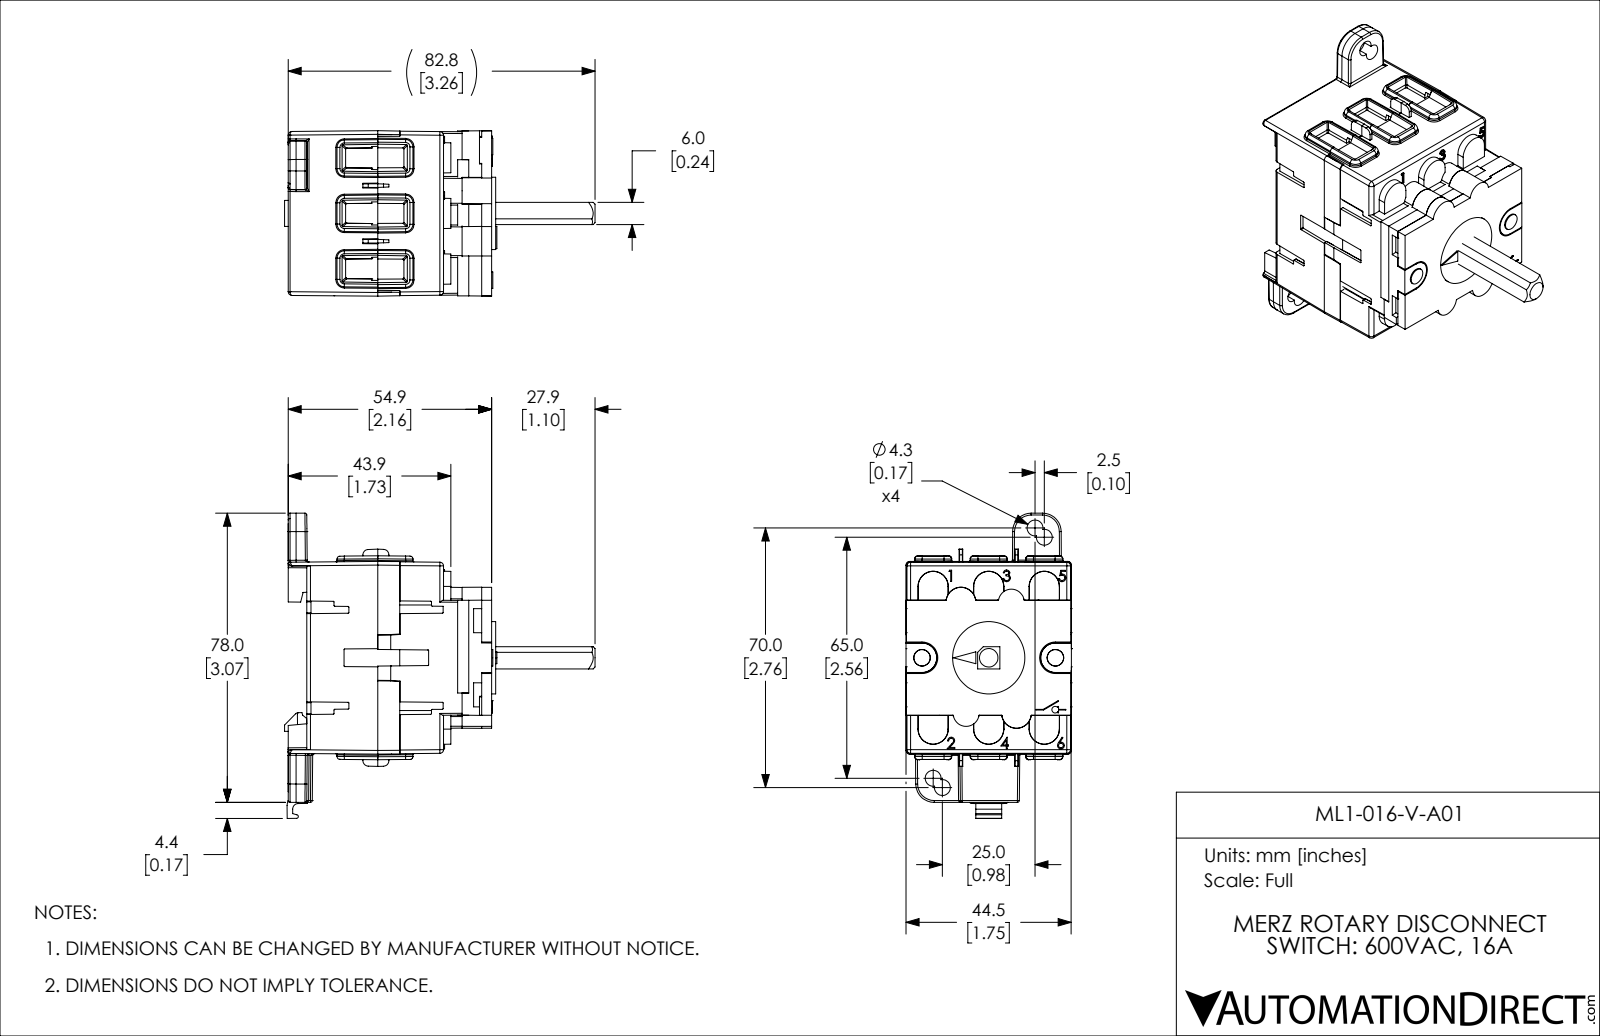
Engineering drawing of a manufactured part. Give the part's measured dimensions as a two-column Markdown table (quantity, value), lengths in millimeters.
| quantity | value |
| --- | --- |
| part name | ML1-016-V-A01 |
| STEP written by | SolidWorks 2019 (AUTOMOTIVE_DESIGN) |
| units | millimeters |
| bodies | 7 solids, 1402 faces (776 planar, 412 cylindrical, 214 other) |
| overall size | 83.8 × 82.3 × 44.6 |
| volume | 124 200 mm³ |
| surface area | 35 010 mm² |
| round holes (diameter × count) | 4.3 × 4, 8 × 1 |
| round bosses / shafts (diameter × count) | 7 × 2, 19.5 × 1, 16.4 × 1, 12 × 1, 8.5 × 1, 8 × 1, 3 × 1 |
| partial cylindrical surfaces (radius × count) | 0.2 × 75, 0.3 × 62, 0.5 × 47, 1 × 29, 0.8 × 28, 0.3 × 12, 2 × 12, 5 × 6 |
| main face-to-face distances | 5.9, 28, 22.1, 41.9, 25.1, 19.2, 47.2, 5.3, 22.8, 16.8 |
| hole center spacings | 3.5, 72.9, 28.3, 28.5, 48.1, 50.2, 71.6, 74.3 |
